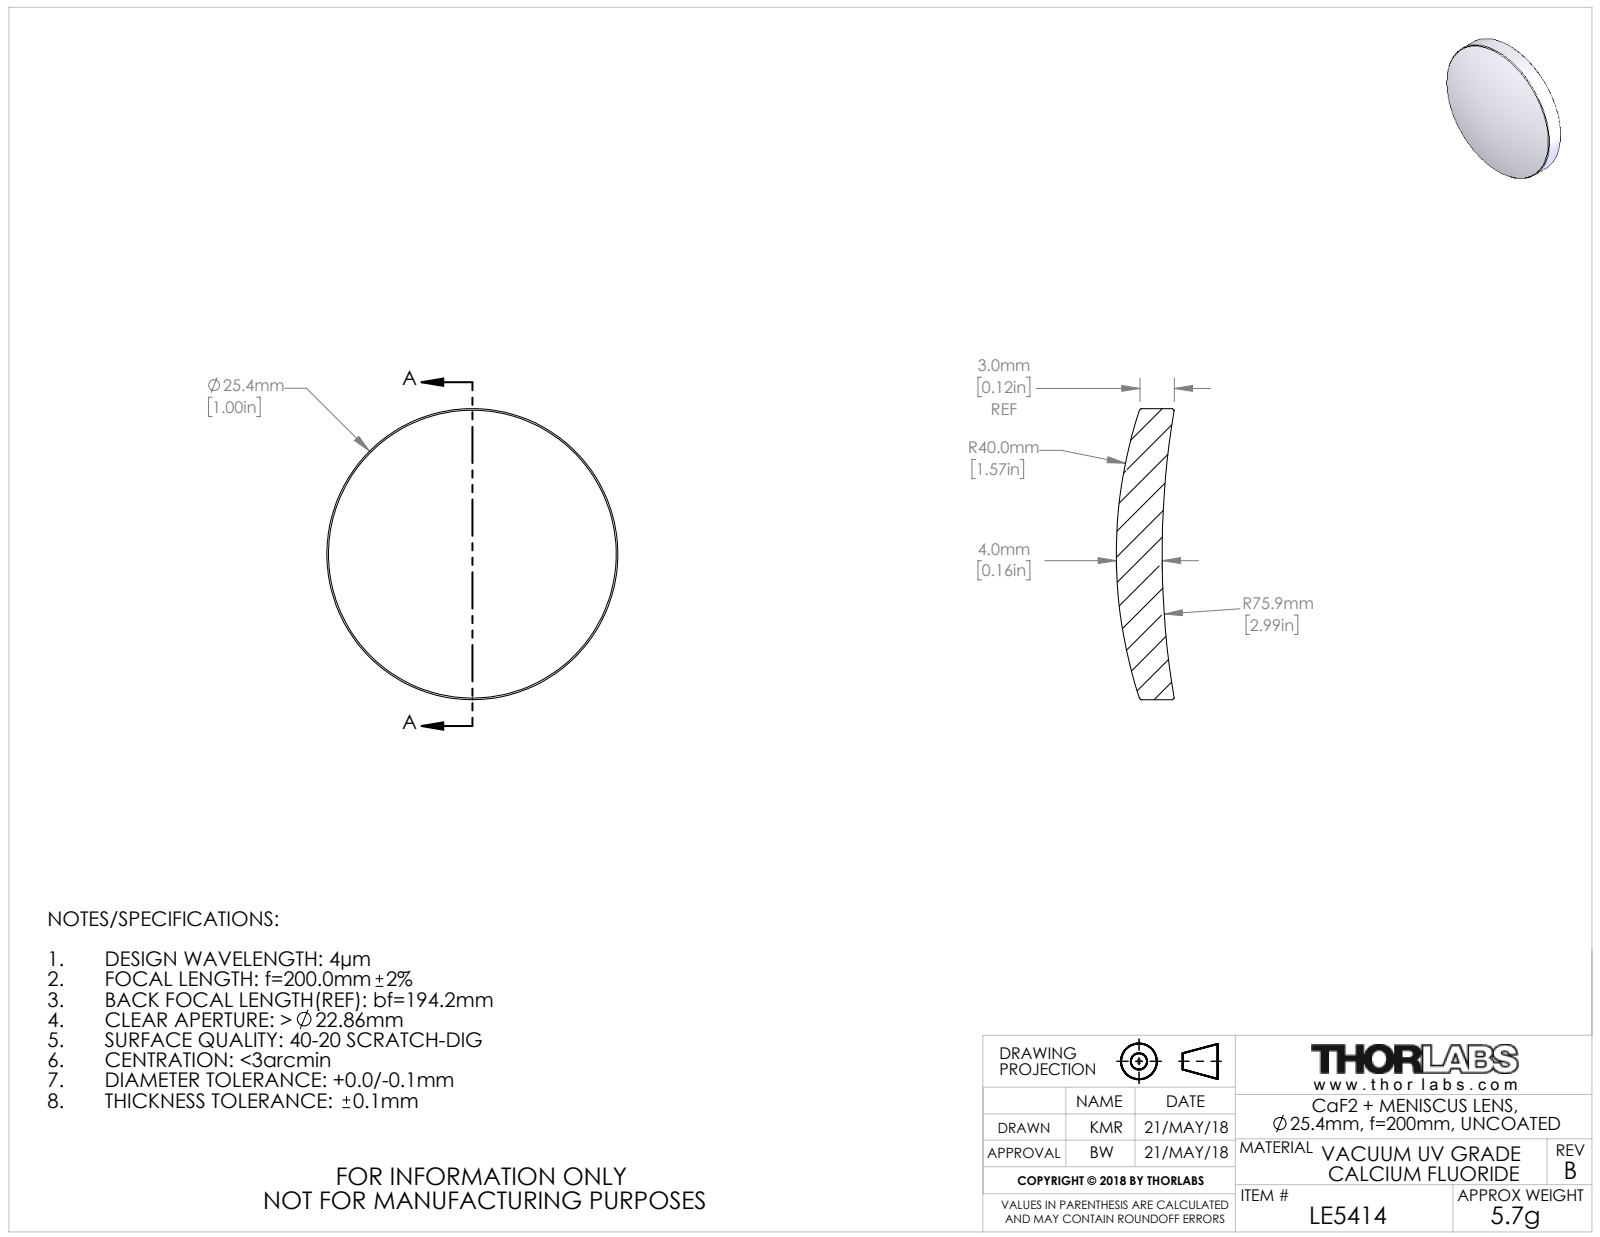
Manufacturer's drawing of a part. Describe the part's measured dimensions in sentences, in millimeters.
The part is named "21991-E0W". Its 3-D file was written by "SolidWorks 2016 (CONFIG_CONTROL_DESIGN)". It is 1 solid with 10 faces: 0 planar, 2 cylindrical and 8 other. Overall it measures 25.4 by 25.4 by 5.1 millimeters. Its volume is 1 770 cubic millimeters and its surface area 1 257 square millimeters. Round bosses or shafts: 1 of diameter 25.4.
